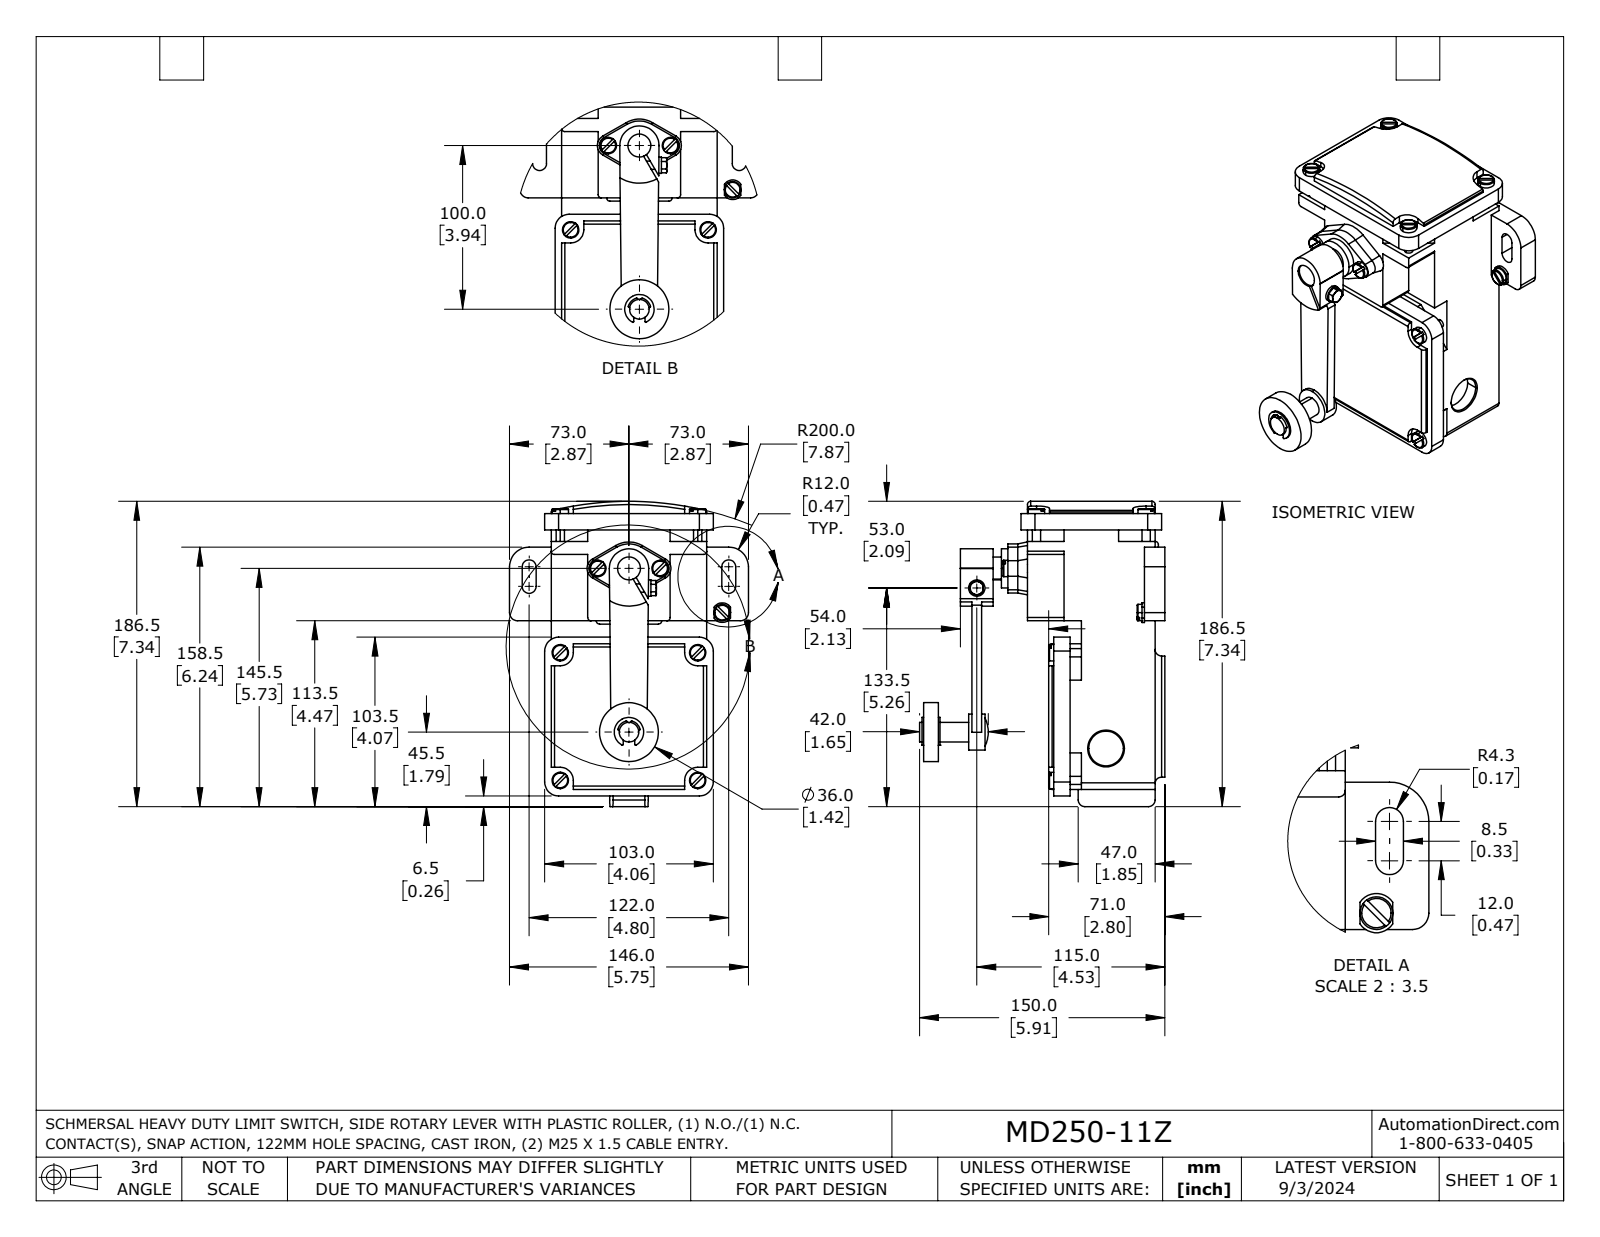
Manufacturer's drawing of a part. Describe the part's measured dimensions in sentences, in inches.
The part is named "MD 250-11Z". Its 3-D file was written by "SolidWorks 2023 (AUTOMOTIVE_DESIGN)". It is 1 solid with 421 faces: 207 planar, 138 cylindrical and 76 other. Overall it measures 7.343 by 5.906 by 5.748 inches. Its volume is 74.88 cubic inches and its surface area 172.6 square inches. Round holes: 1 of diameter 0.163, 1 of diameter 0.197, 1 of diameter 0.551, 1 of diameter 0.833. Round bosses or shafts: 12 of diameter 0.394, 8 of diameter 0.197, 1 of diameter 2.913, 1 of diameter 1.417, 1 of diameter 0.945, 1 of diameter 0.866, 1 of diameter 0.709, 1 of diameter 0.472. Partial cylindrical surfaces (rounded edges, fillets, slot ends): 10 of radius 0.079, 8 of radius 0.315, 8 of radius 0.335, 6 of radius 0.02, 4 of radius 0.157, 4 of radius 0.167, 2 of radius 0.039, 2 of radius 0.197. The main face-to-face distances are 0.236, 2.559, 3.74, 2.795, 0.512, 0.157, 0.394, 0.276, 0.669, 0.787. The hole center spacings are 4.956.
